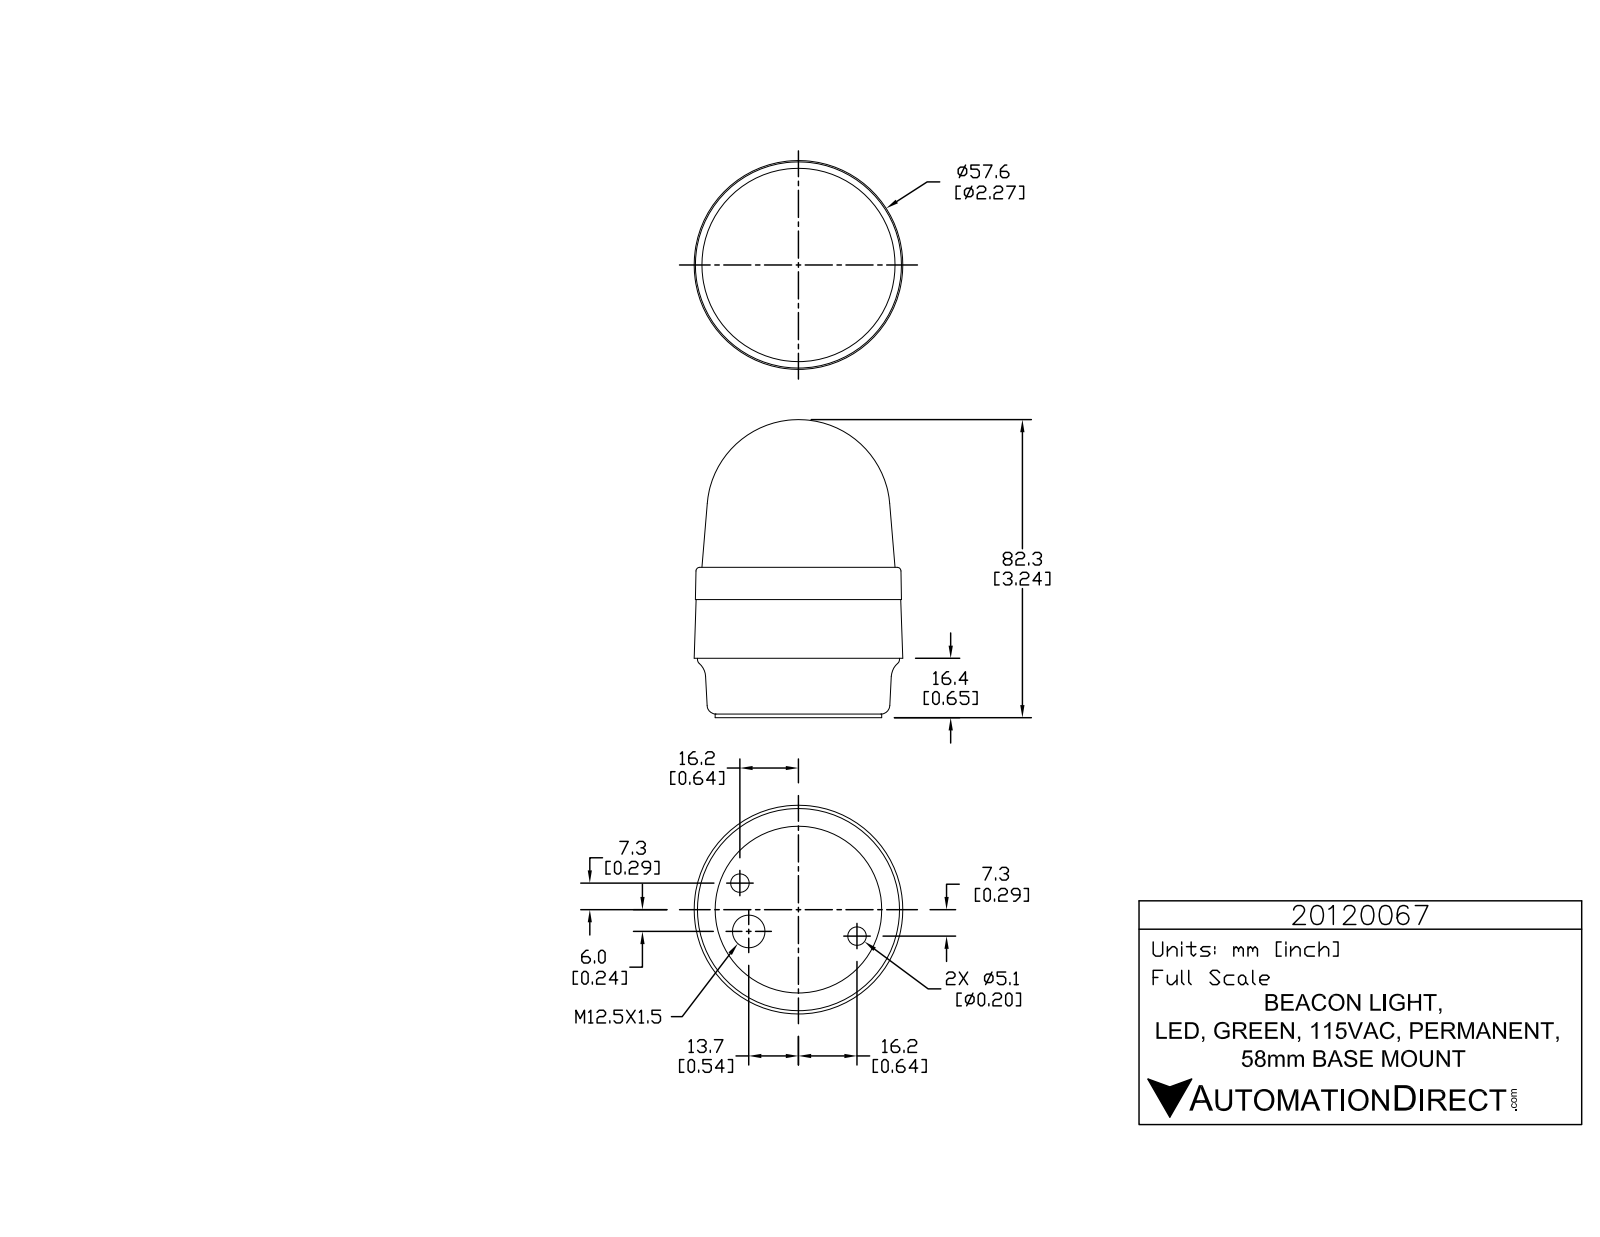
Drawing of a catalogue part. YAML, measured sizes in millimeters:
part_name: "20120067"
step_written_by: "SolidWorks 2015 (AUTOMOTIVE_DESIGN)"
units: millimeters
bodies: {solids: 1, faces: 763, planar: 527, cylindrical: 145, other: 91}
overall_size: [82.3, 57.63, 57.63]
volume: 164395
surface_area: 16261
round_holes:
  - {diameter: 0.99, count: 3}
  - {diameter: 5.11, count: 2}
  - {diameter: 9, count: 1}
round_bosses_or_shafts:
  - {diameter: 5.74, count: 3}
  - {diameter: 1.43, count: 3}
  - {diameter: 55.8, count: 1}
  - {diameter: 46, count: 1}
partial_cylinders:
  - {radius: 0.2, count: 6}
  - {radius: 0.21, count: 6}
  - {radius: 0.21, count: 6}
  - {radius: 3.32, count: 6}
  - {radius: 0.1, count: 3}
  - {radius: 0.12, count: 3}
  - {radius: 0.19, count: 3}
  - {radius: 0.2, count: 3}
face_to_face_distances: [16.4, 1, 15.4, 41.5, 40.5, 25.1, 32.6, 31.6, 16.2, 8.9]
hole_center_spacings: [13.56, 29.94, 35.5]
